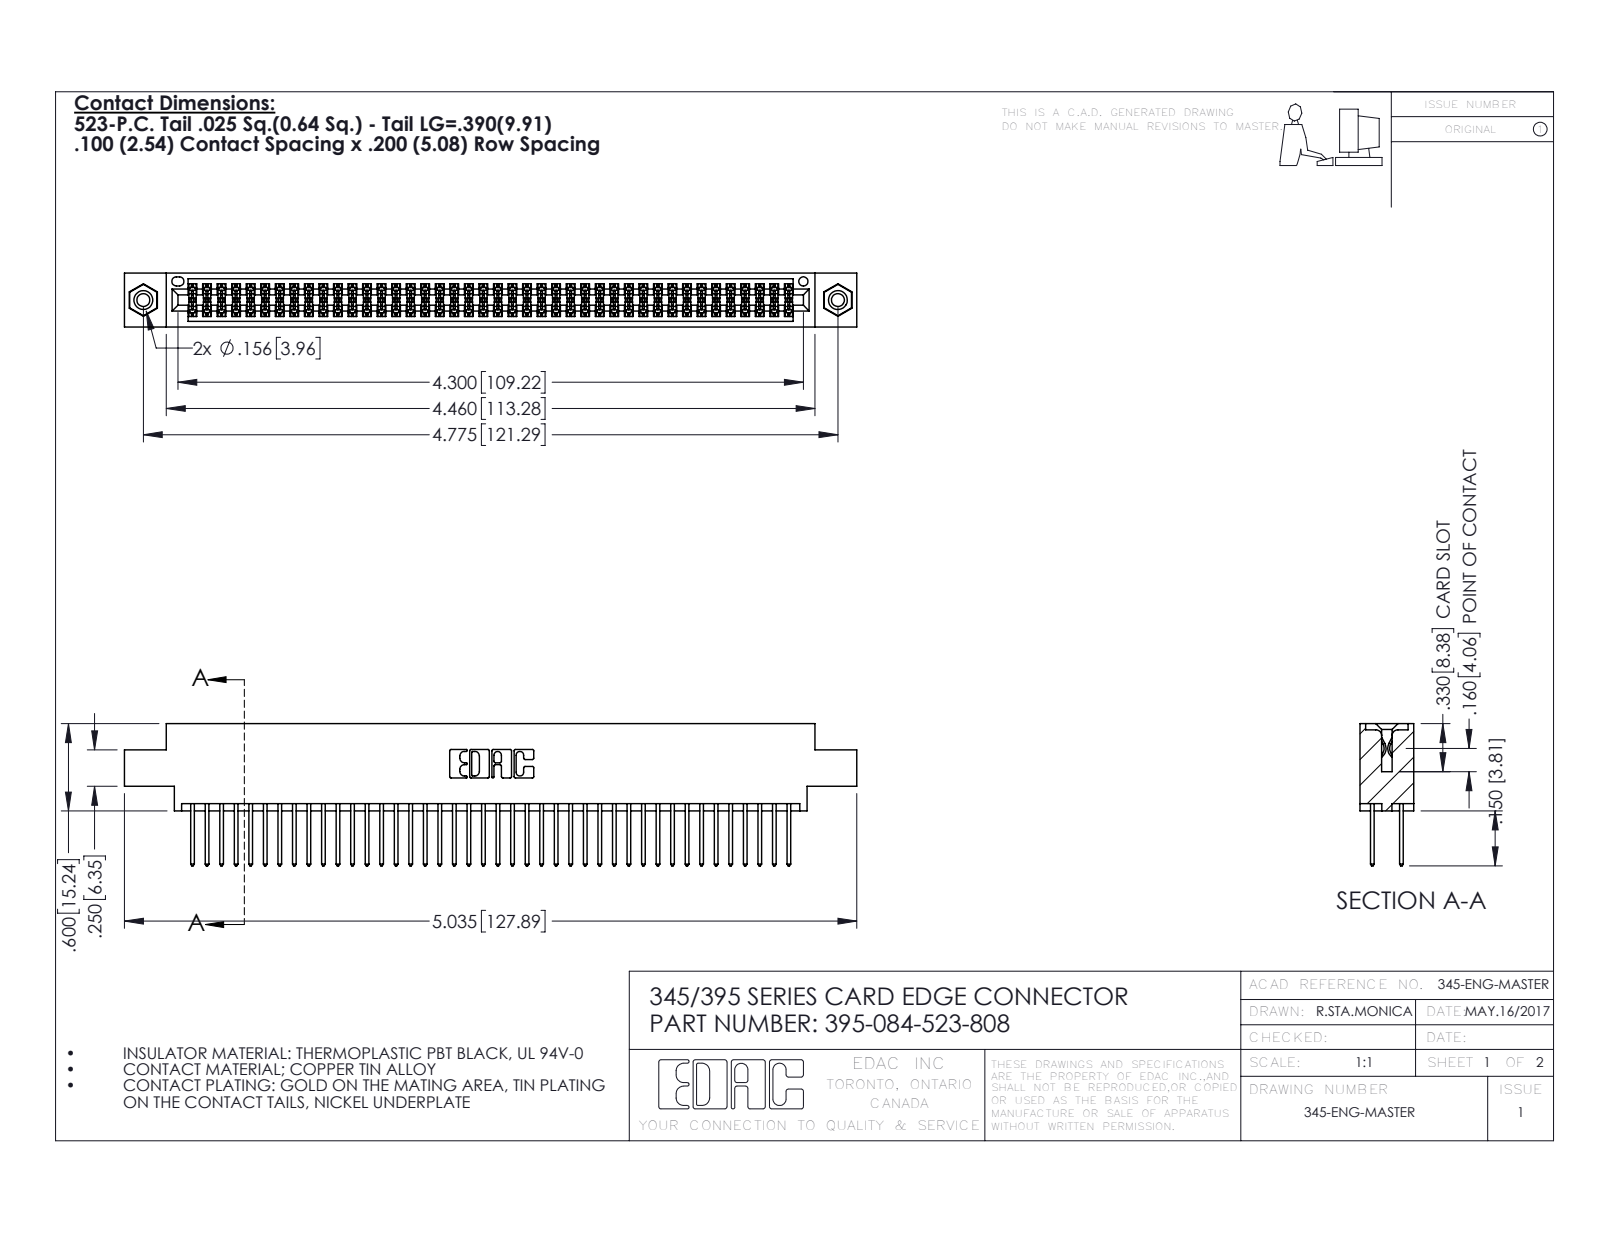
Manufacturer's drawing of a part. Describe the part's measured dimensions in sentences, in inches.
The part is named "345 Part_0.170 Offset - 0.156 Dia-TI; 345-250-001_345-250-003-102; 345-292-001_345-293-123; 395-084-523-808". Its 3-D file was written by "SolidWorks 2016 (CONFIG_CONTROL_DESIGN)". It is 87 solids with 4390 faces: 2888 planar, 1486 cylindrical and 16 other. Overall it measures 5.035 by 0.977 by 0.37 inches. Its volume is 0.761 cubic inches and its surface area 30.02 square inches. Round holes: 2 of diameter 0.089, 2 of diameter 0.125, 2 of diameter 0.156, 1 of diameter 0.064. Round bosses or shafts: 2 of diameter 0.155. Partial cylindrical surfaces (rounded edges, fillets, slot ends): 126 of radius 0.006, 84 of radius 0.01, 22 of radius 0.01, 6 of radius 0.007, 6 of radius 0.031, 3 of radius 0.026, 2 of radius 0.014, 2 of radius 0.019. The main face-to-face distances are 0.072, 0.298, 0.2, 0.098, 0.272, 0.025, 0.37, 0.225, 0.175, 0.149. The hole center spacings are 0.27, 4.539, 4.775.
